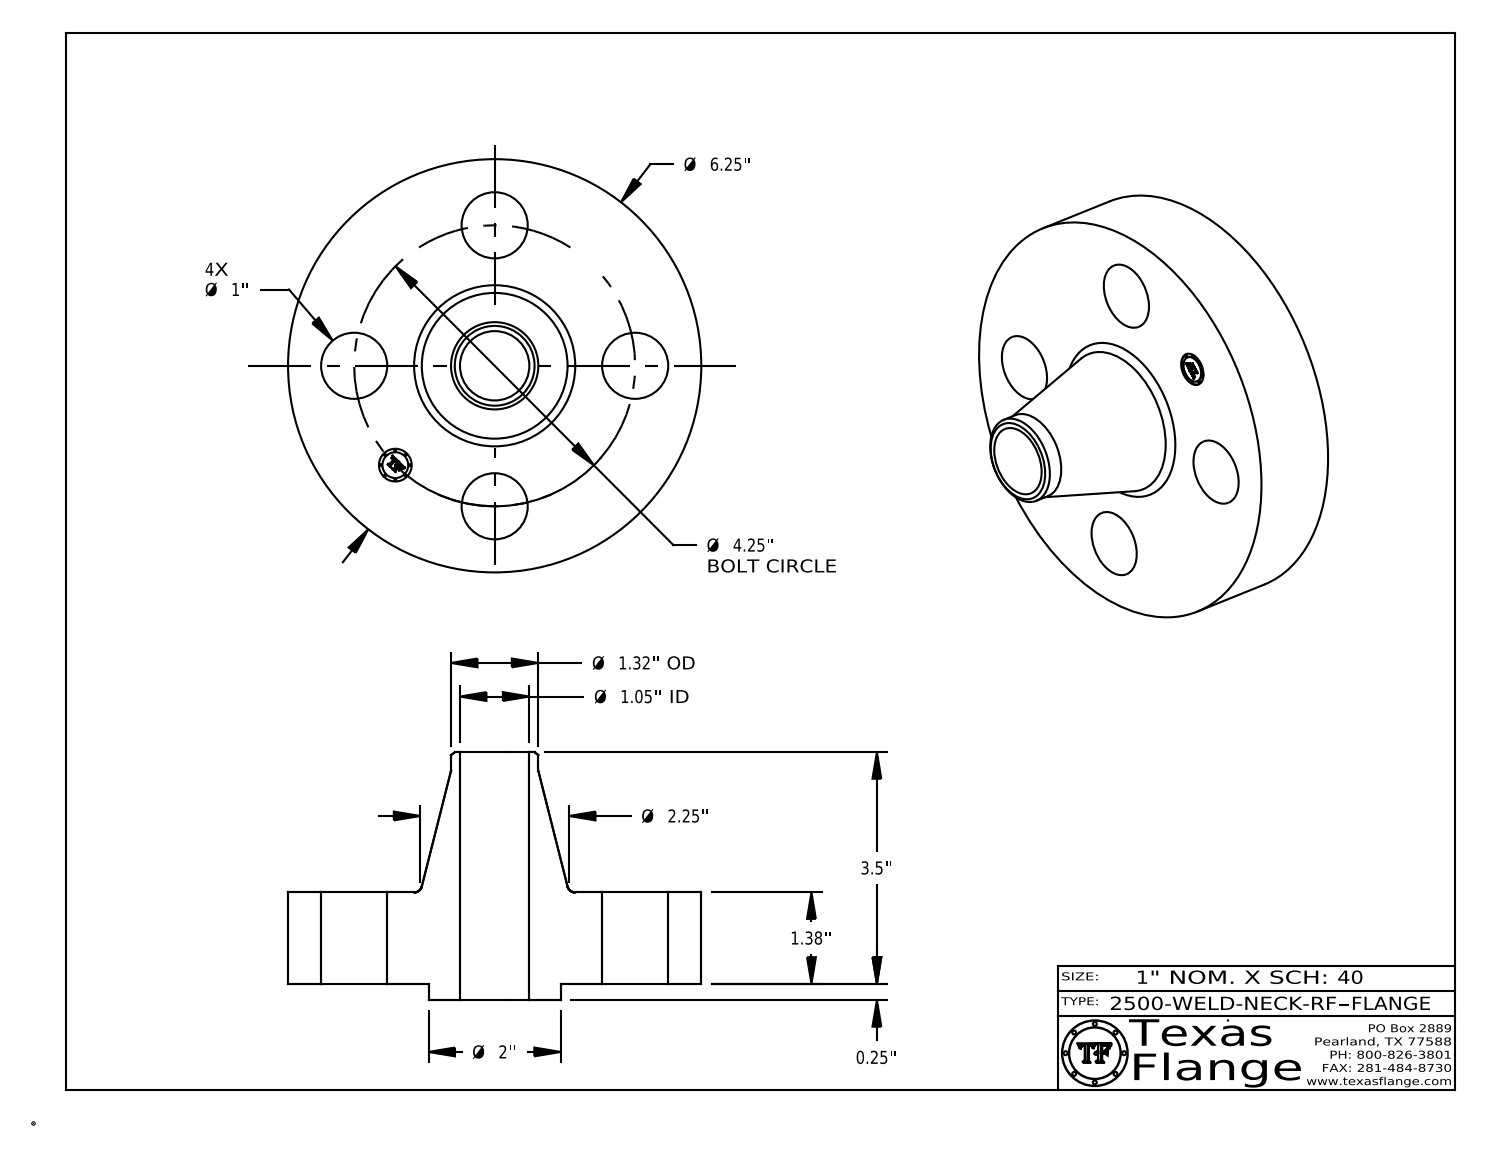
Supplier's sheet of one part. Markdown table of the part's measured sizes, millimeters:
| quantity | value |
| --- | --- |
| part name | 2500-WELD-NECK-RF |
| STEP written by | CATIA V5 STEP AP214 (AUTOMOTIVE_DESIGN) |
| units | millimeters |
| bodies | 1 solid, 411 faces (369 planar, 36 cylindrical, 6 other) |
| overall size | 158.8 × 158.8 × 95.3 |
| volume | 666 000 mm³ |
| surface area | 77 870 mm² |
| round holes (diameter × count) | 25.4 × 4, 12.6 × 1, 26.6 × 1 |
| round bosses / shafts (diameter × count) | 0.8 × 8, 158.8 × 1, 50.8 × 1, 33.5 × 1, 9.9 × 1 |
| main face-to-face distances | 35.1, 6.4, 41.4, 95.3, 88.9, 53.8, 41, 34.7, 0.4, 54.2 |
| hole center spacings | 54, 76.4, 41.3, 99.7, 108 |
